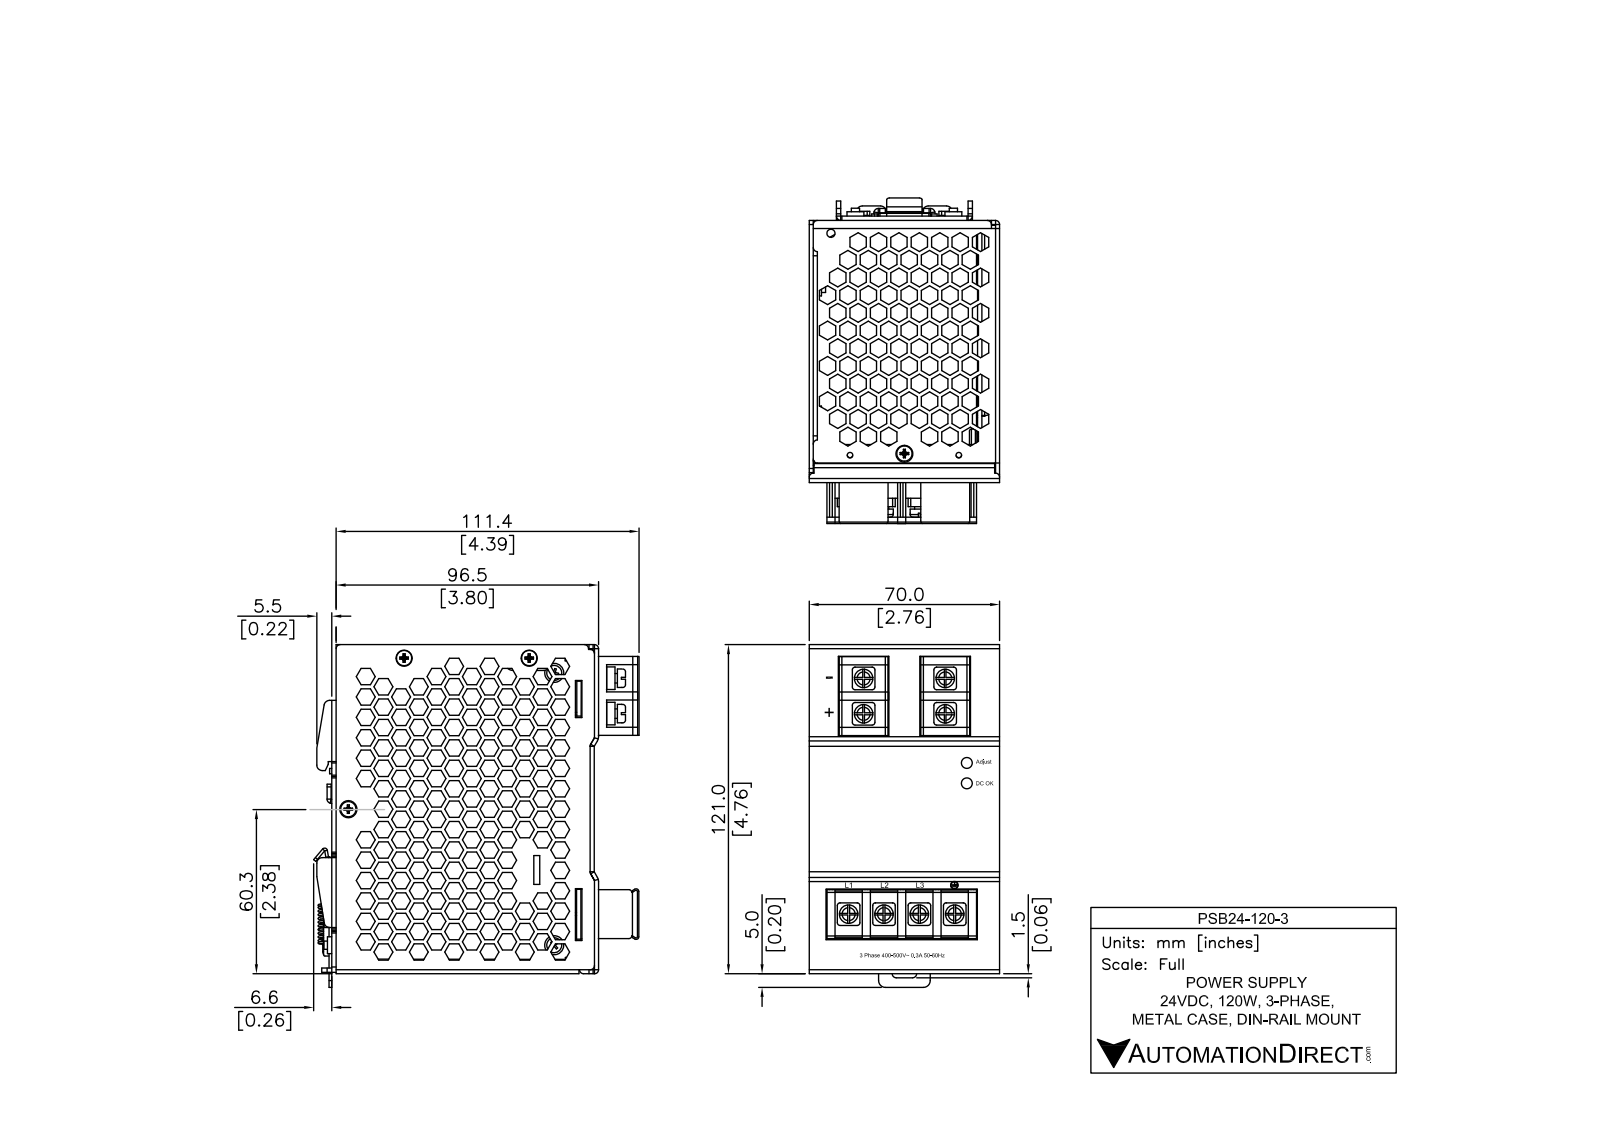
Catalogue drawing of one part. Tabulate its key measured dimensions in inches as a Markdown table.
| quantity | value |
| --- | --- |
| part name | PSB24-120-3 |
| STEP written by | SolidWorks 2011 (CONFIG_CONTROL_DESIGN) |
| units | inches |
| bodies | 2 solids, 3915 faces (3736 planar, 96 cylindrical, 83 other) |
| overall size | 4.946 × 4.572 × 2.76 |
| volume | 44.96 in³ |
| surface area | 245.1 in² |
| round holes (diameter × count) | 0.145 × 2 |
| round bosses / shafts (diameter × count) | 0.23 × 4, 0.205 × 4, 0.125 × 4 |
| partial cylindrical surfaces (radius × count) | 0.06 × 21, 0.03 × 12, 0.05 × 8, 0.04 × 2, 0.075 × 2, 0.13 × 2, 0.01 × 1, 0.07 × 1 |
| main face-to-face distances | 0.148, 2.608, 0.07, 0.078, 2.678, 2.53, 2.46, 0.06, 0.075, 3.583 |
| hole center spacings | 0.3 |
